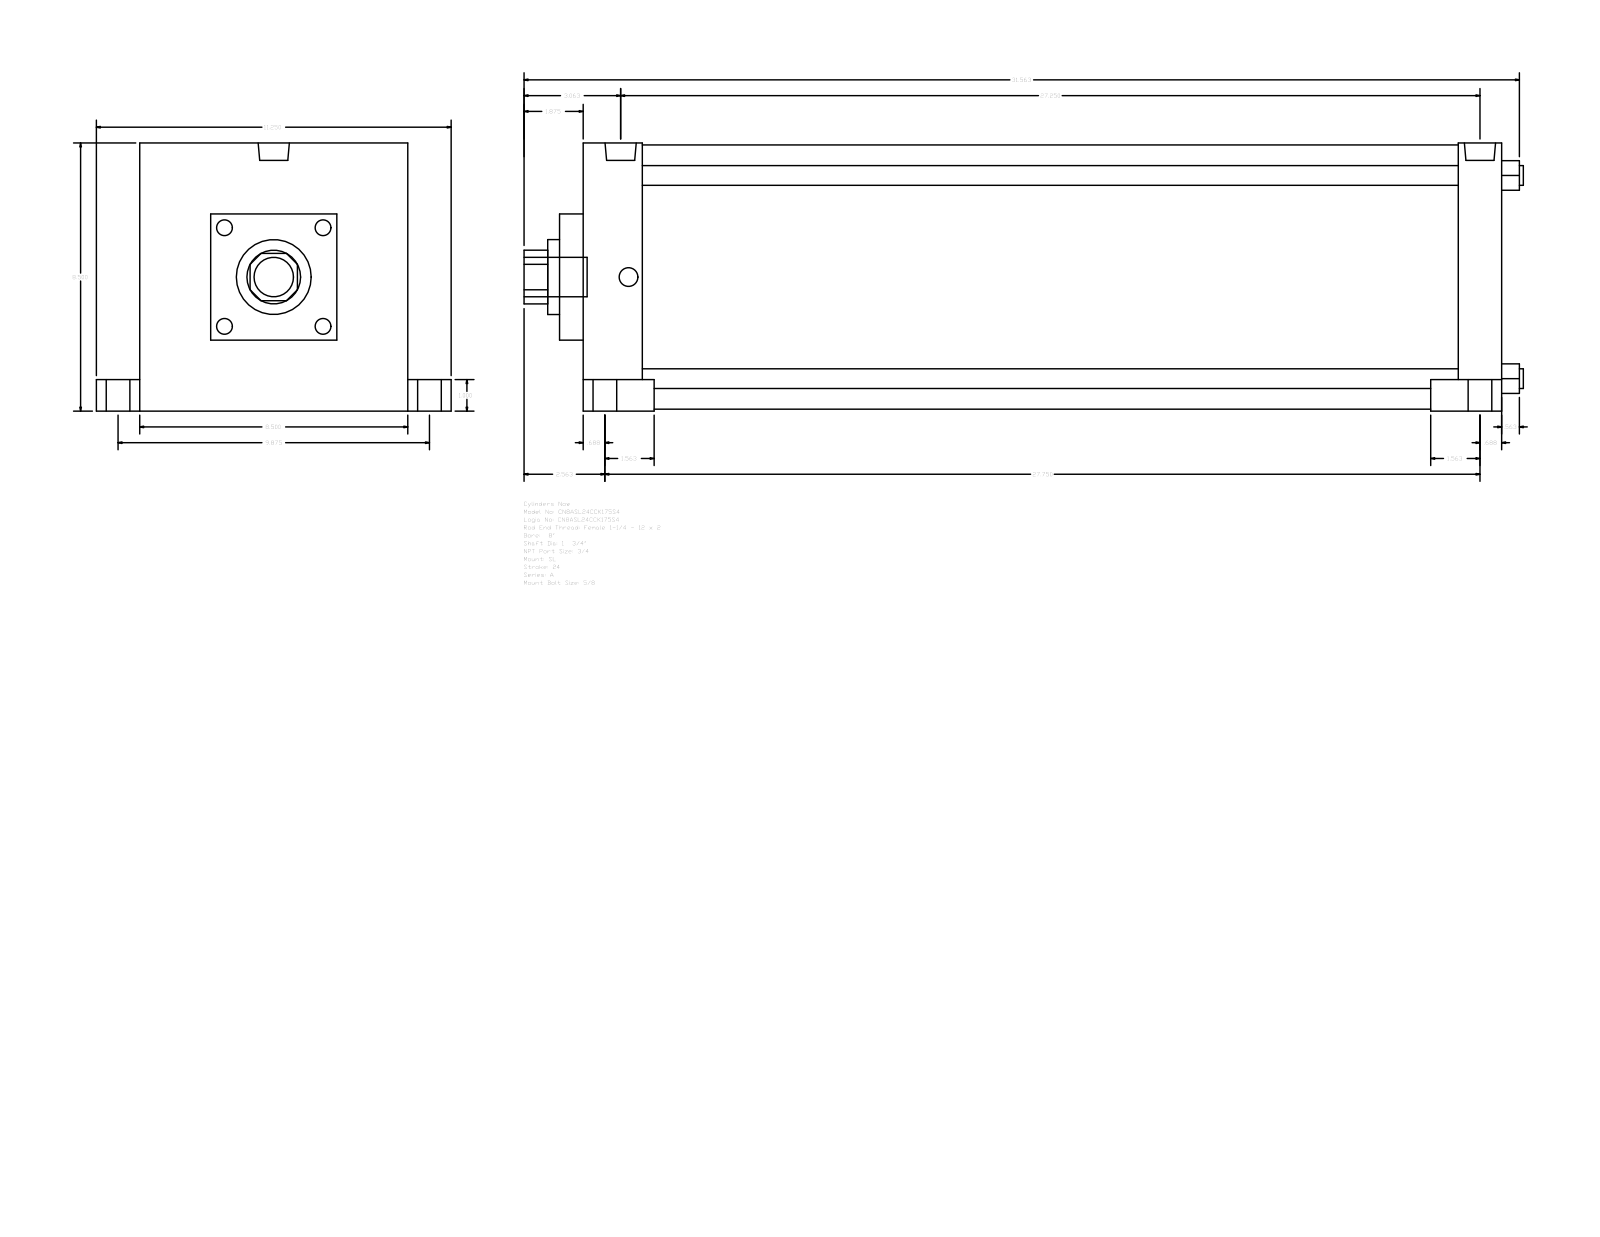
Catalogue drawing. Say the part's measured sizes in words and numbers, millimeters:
The part is named "A_SL__0800_1.75". Its 3-D file was written by "GSSL Pune (CONFIG_CONTROL_DESIGN)". It is 0 solids with 117 faces: 85 planar, 32 cylindrical and 0 other. Overall it measures 804.86 by 285.75 by 215.9 millimeters. Round holes: 4 of diameter 15.88, 1 of diameter 44.45, 1 of diameter 60.33, 1 of diameter 212.72. Round bosses or shafts: 4 of diameter 25.4, 4 of diameter 19.05, 4 of diameter 15.08, 2 of diameter 25.12, 1 of diameter 31.75. Partial cylindrical surfaces (rounded edges, fillets, slot ends): 1 of radius 21.63. The main face-to-face distances are 739.78, 215.9, 34.92, 47.63, 692.15, 704.86, 657.23, 57.15, 19.05, 158.75. The hole center spacings are 115.67, 163.58, 231.34.
